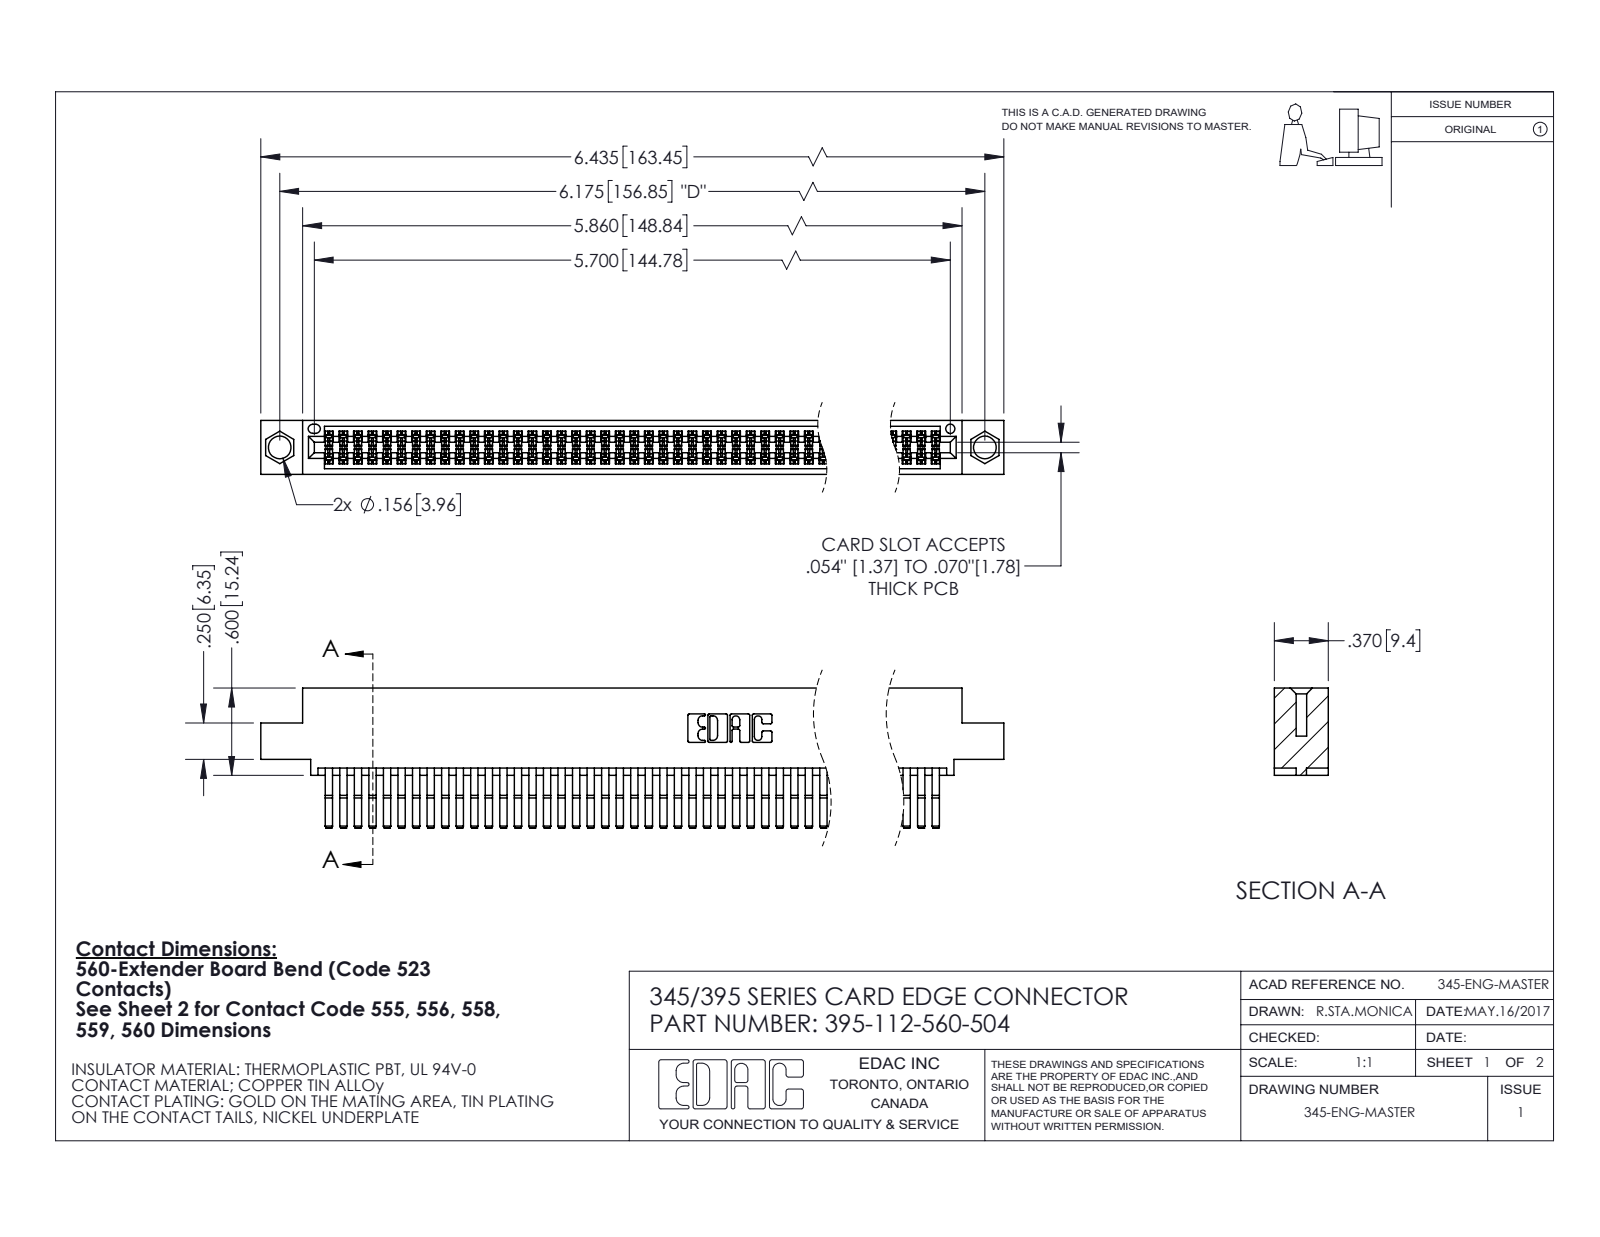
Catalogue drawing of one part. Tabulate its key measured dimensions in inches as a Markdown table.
| quantity | value |
| --- | --- |
| part name | 345-292-001_560 Tail; 345 Part_0.110 Offset - 0.156 Dia-TI; 395-112-560-504 |
| STEP written by | SolidWorks 2020 (CONFIG_CONTROL_DESIGN) |
| units | inches |
| bodies | 113 solids, 5968 faces (3794 planar, 2174 cylindrical, 0 other) |
| overall size | 6.435 × 0.962 × 0.37 |
| volume | 1.011 in³ |
| surface area | 41.21 in² |
| round holes (diameter × count) | 0.156 × 2, 0.064 × 1 |
| partial cylindrical surfaces (radius × count) | 0.006 × 168, 0.01 × 22, 0.007 × 6, 0.031 × 6, 0.026 × 3, 0.01 × 2, 0.014 × 2, 0.019 × 2 |
| main face-to-face distances | 0.025, 0.298, 0.072, 0.37, 0.2, 0.098, 0.272, 0.225, 0.175, 0.149 |
| hole center spacings | 0.27, 5.939, 6.175 |
